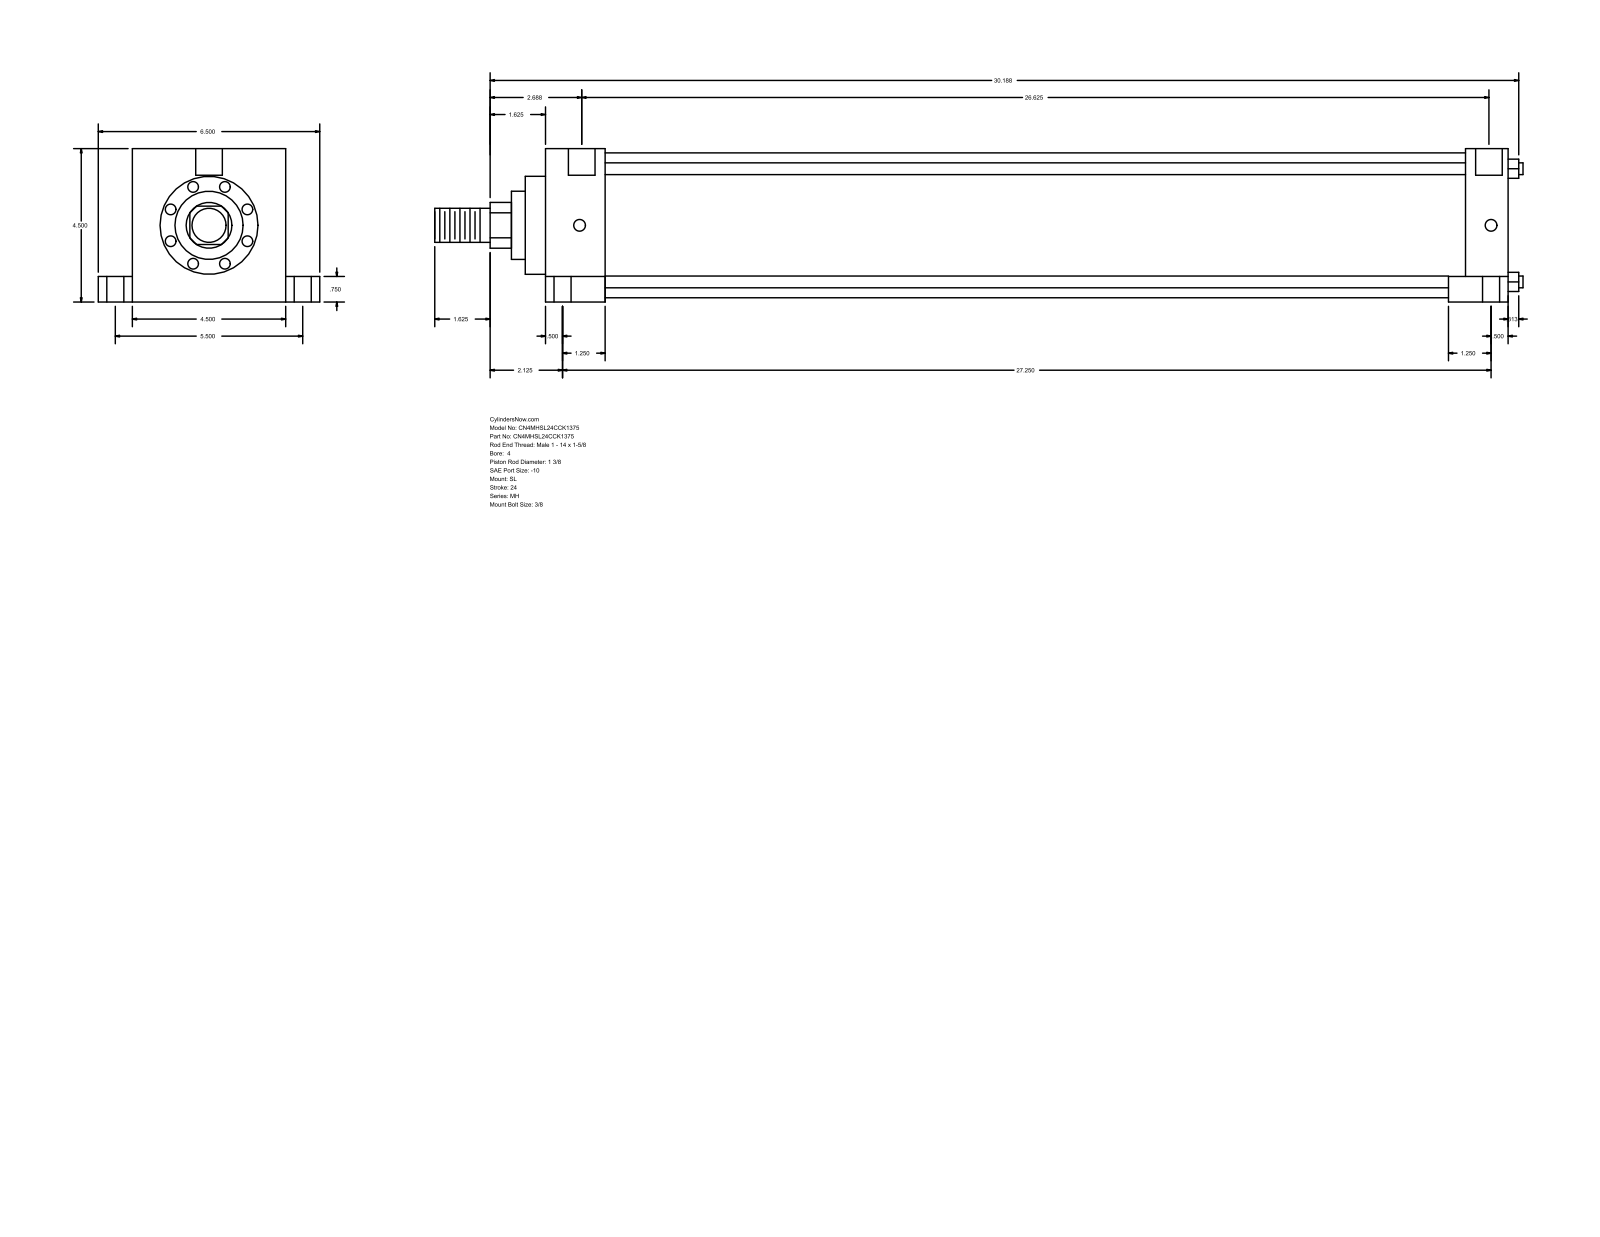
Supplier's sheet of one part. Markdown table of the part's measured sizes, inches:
| quantity | value |
| --- | --- |
| part name | MH_SL__0400_1.375 |
| STEP written by | GSSL Pune (CONFIG_CONTROL_DESIGN) |
| units | inches |
| bodies | 0 solids, 110 faces (77 planar, 33 cylindrical, 0 other) |
| overall size | 31.937 × 6.5 × 4.5 |
| round holes (diameter × count) | 0.344 × 4, 0.5 × 4, 0.75 × 4, 0.781 × 2 |
| round bosses / shafts (diameter × count) | 0.345 × 4, 4.25 × 1, 2.875 × 1, 2 × 1, 1.375 × 1, 1 × 1 |
| partial cylindrical surfaces (radius × count) | 0.672 × 1 |
| main face-to-face distances | 4.5, 28.25, 1.75, 26.5, 27, 25.25, 1.25, 1, 5.5, 0.75 |
| hole center spacings | 2.75, 2.751, 2.795, 2.807, 5.5, 26.75, 26.829, 26.891 |
